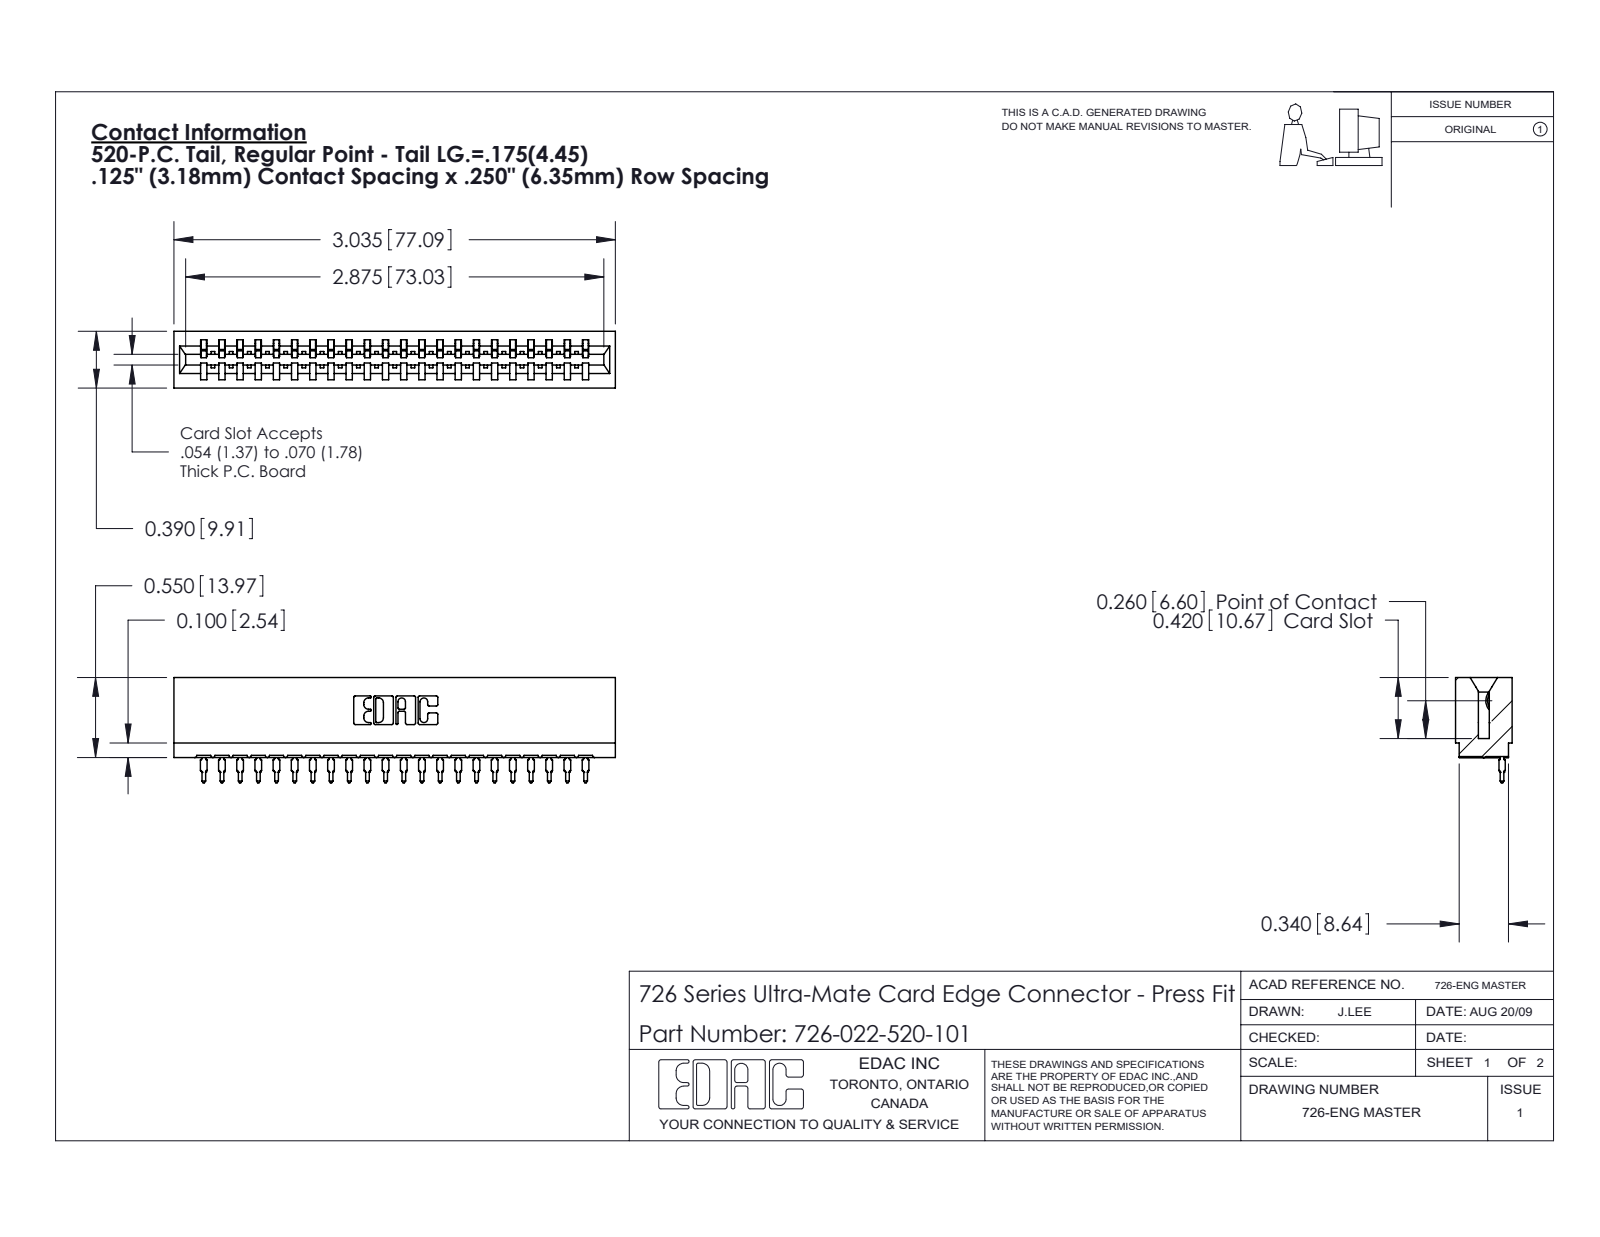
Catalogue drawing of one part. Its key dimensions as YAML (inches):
part_name: "726-022-520-101; 746-292-001_520; 726 Part_.515 Slot Depth - 01"
step_written_by: "SolidWorks 2020 (CONFIG_CONTROL_DESIGN)"
units: inches
bodies: {solids: 23, faces: 2473, planar: 1441, cylindrical: 460, other: 572}
overall_size: [3.035, 0.724, 0.39]
volume: 0.425
surface_area: 15.78
partial_cylinders:
  - {radius: 0.021, count: 44}
  - {radius: 0.015, count: 23}
  - {radius: 0.01, count: 22}
  - {radius: 0.007, count: 6}
  - {radius: 0.031, count: 6}
  - {radius: 0.005, count: 4}
  - {radius: 0.011, count: 4}
  - {radius: 0.026, count: 3}
face_to_face_distances: [0.057, 0.333, 0.39, 0.025, 0.307, 0.25, 0.042, 1.25, 0.125, 0.5]
